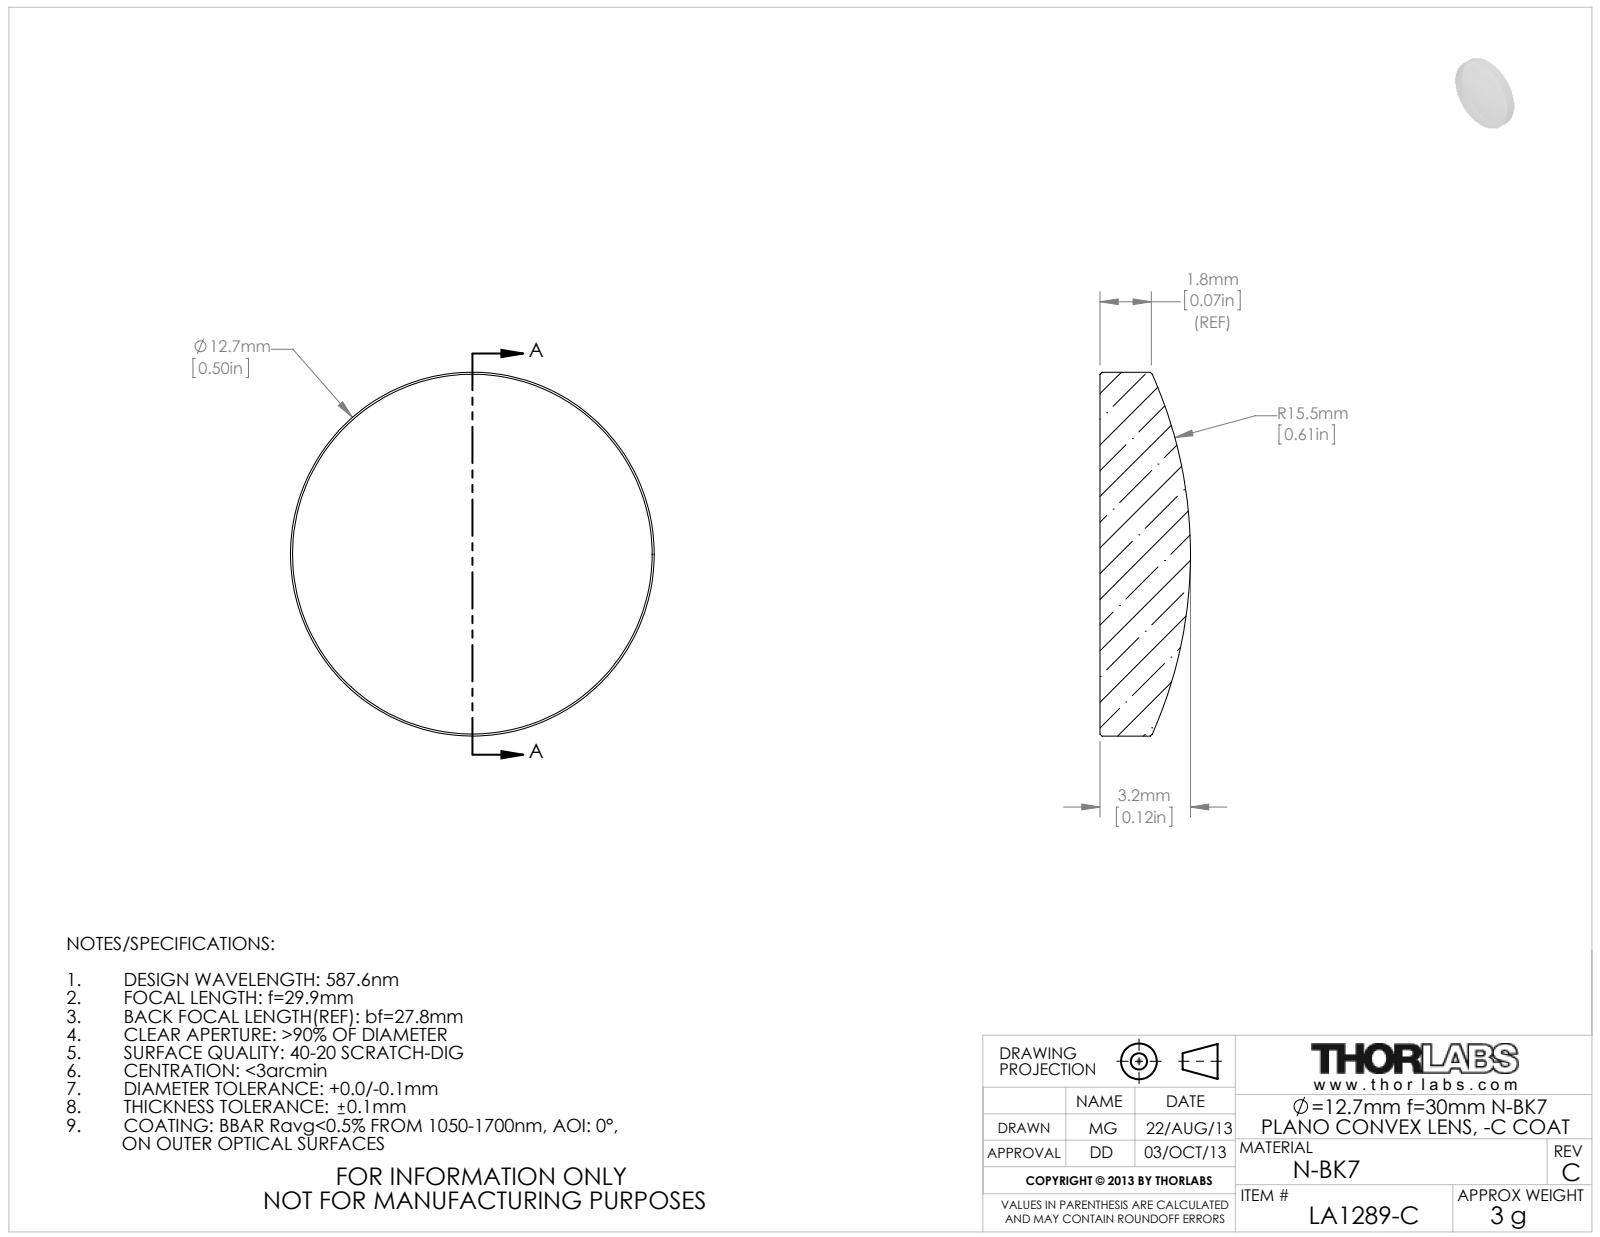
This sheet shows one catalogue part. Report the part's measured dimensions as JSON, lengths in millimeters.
{"part_name": "4569-E0W", "step_written_by": "SolidWorks 2009 (AUTOMOTIVE_DESIGN)", "units": "millimeters", "bodies": {"solids": 1, "faces": 5, "planar": 1, "cylindrical": 2, "other": 2}, "overall_size": [12.7, 12.7, 3.16], "volume_mm3": 315, "surface_area_mm2": 331, "round_bosses_or_shafts": [[12.7, 1]]}
